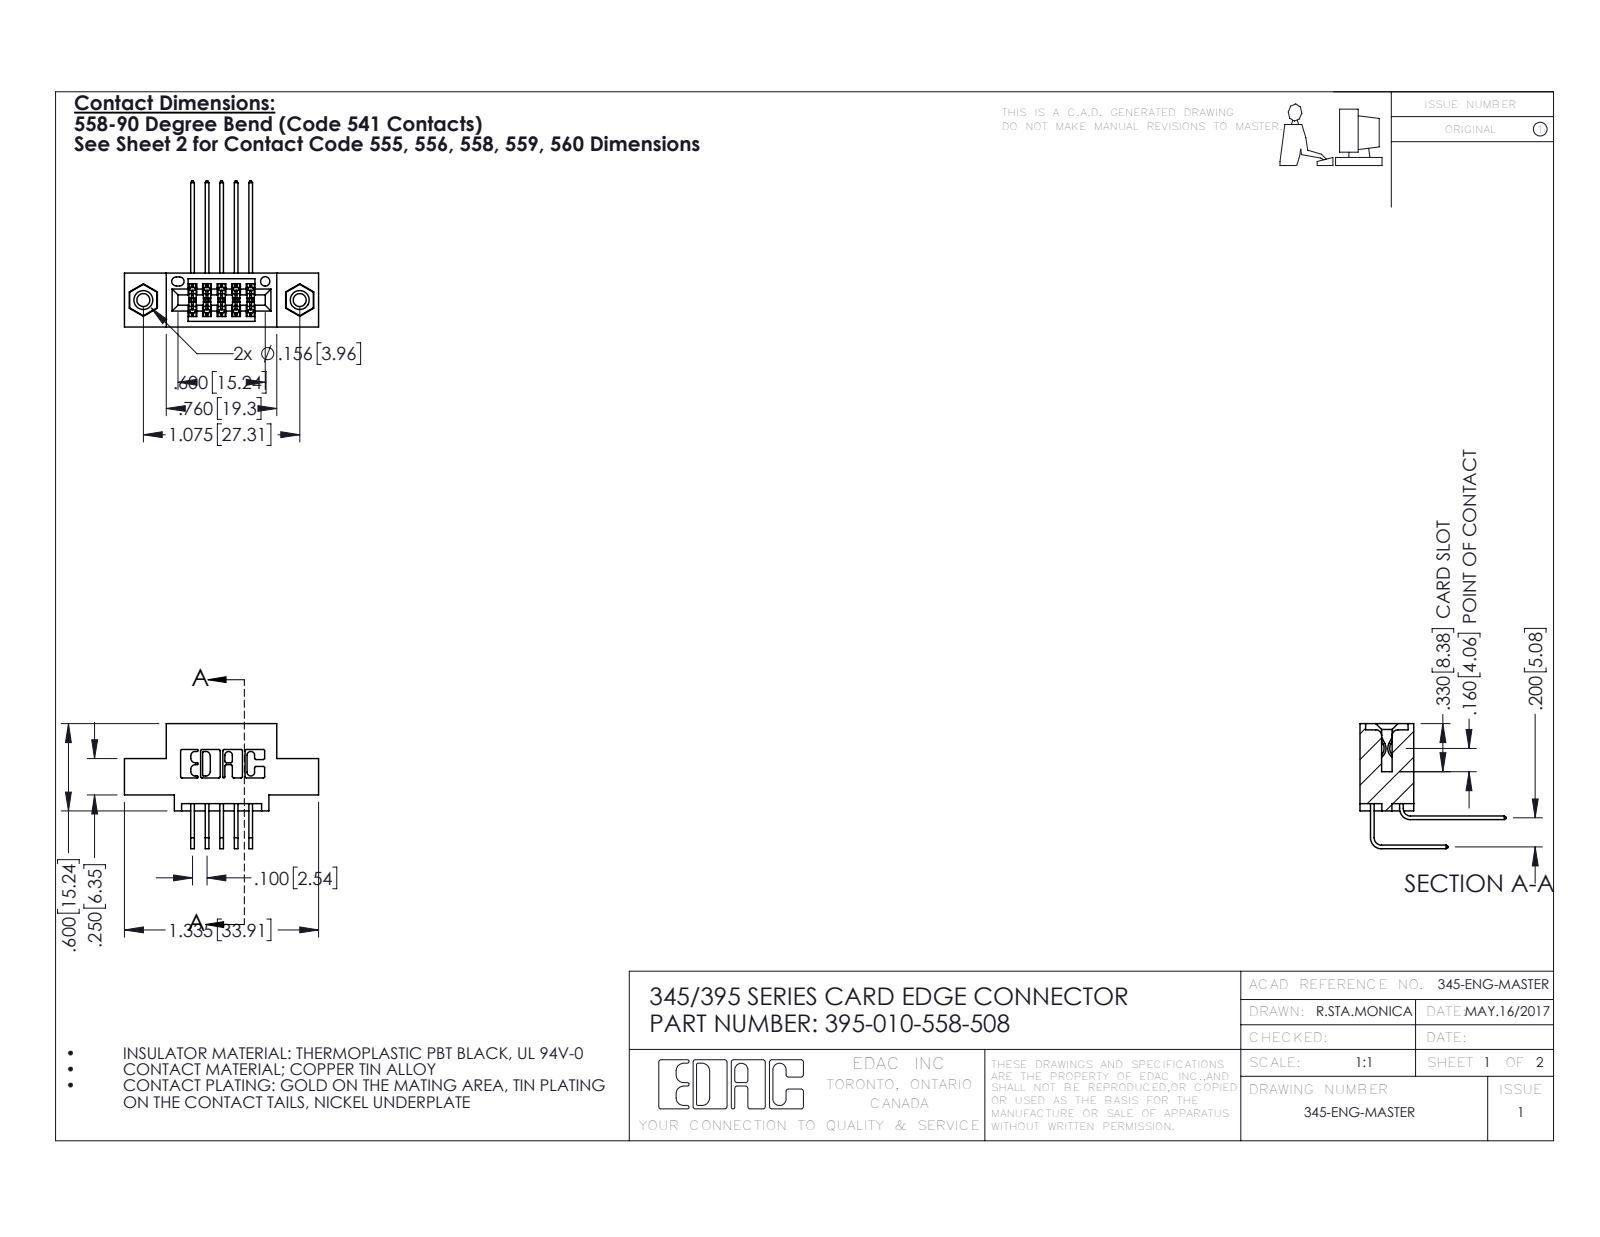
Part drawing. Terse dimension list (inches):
name: 345-250-001_345-250-003-102; 345 Part_0.110 Offset - 0.156 Dia-TI; 345-292-001_558 Tail - 2; 345-292-001_558 559 Tail - 1 (+1 more)
written by: SolidWorks 2016 (CONFIG_CONTROL_DESIGN)
unit: in
bodies: 13 solids, 710 faces (466 planar, 228 cylindrical, 16 other)
size: 1.335 × 1.005 × 0.859
volume: 0.179 in³; area: 6.184 in²
holes: 2× ⌀0.089, 2× ⌀0.125, 2× ⌀0.156, 1× ⌀0.064
bosses: 2× ⌀0.155
rounds: 22× R0.01, 16× R0.006, 6× R0.007, 6× R0.031, 3× R0.026, 2× R0.014, 2× R0.019, 2× R0.022
face distances: 0.2, 0.37, 0.1, 0.072, 0.298, 0.098, 0.272, 0.025, 0.25, 0.06
hole spacings: 0.27, 0.847, 1.075
